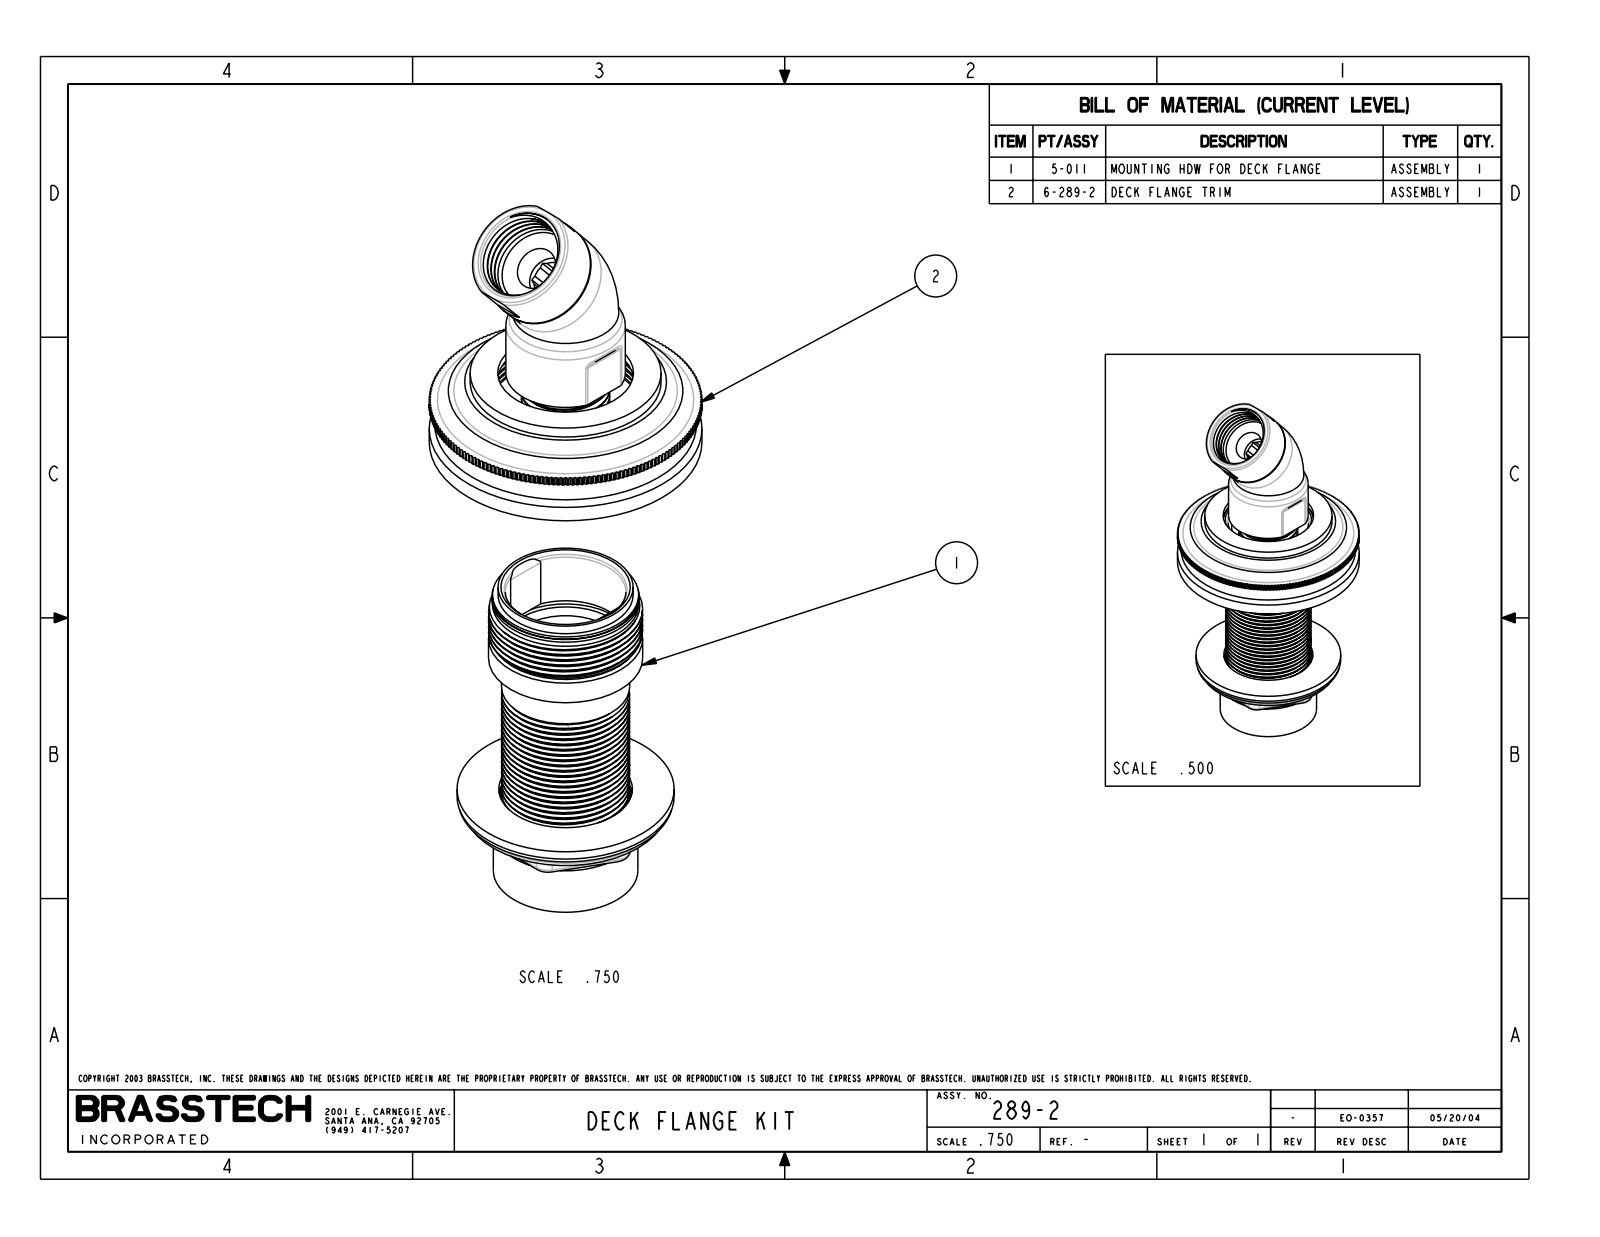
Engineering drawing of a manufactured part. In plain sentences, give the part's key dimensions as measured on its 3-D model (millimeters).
The part is named "289-2_WEB". Its 3-D file was written by "PRO/ENGINEER BY PARAMETRIC TECHNOLOGY CORPORATION, 2009300 (CONFIG_CONTROL_DESIGN)". It is 0 solids with 739 faces: 389 planar, 294 cylindrical and 56 other. Overall it measures 131.6 by 63.5 by 63.5 millimeters. Round bosses or shafts: 1 of diameter 63.5, 1 of diameter 61, 1 of diameter 50, 1 of diameter 48.1, 1 of diameter 44.5, 1 of diameter 35.9, 1 of diameter 33.7, 1 of diameter 29.8. Partial cylindrical surfaces (rounded edges, fillets, slot ends): 6 of radius 1, 6 of radius 1.3, 6 of radius 3.8. The main face-to-face distances are 2.5, 5.1, 12.1, 10.2, 1.9, 7.6, 62.5, 14.6, 4.4, 1.
